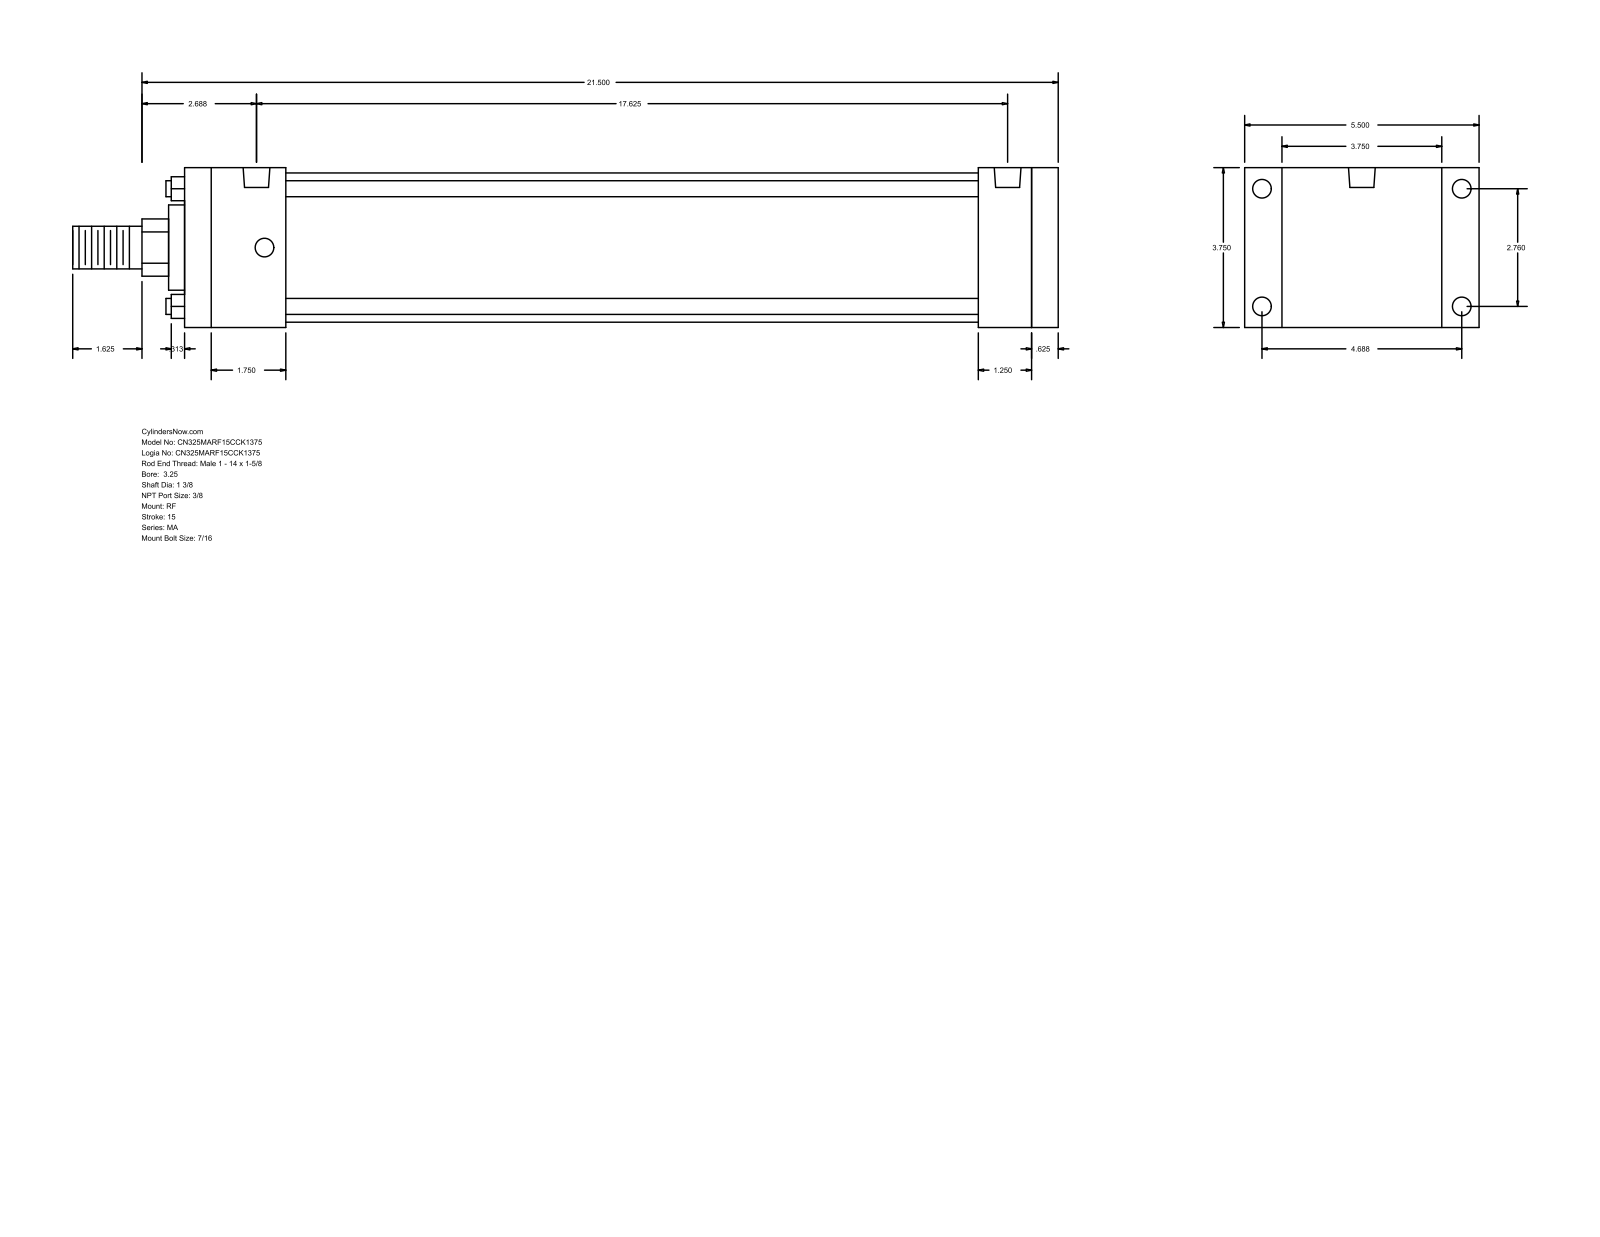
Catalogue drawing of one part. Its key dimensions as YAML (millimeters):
part_name: "MA_RF__0325_1.375"
step_written_by: "GSSL Pune (CONFIG_CONTROL_DESIGN)"
units: millimeters
bodies: {solids: 0, faces: 92, planar: 64, cylindrical: 28, other: 0}
overall_size: [587.38, 139.7, 95.25]
round_holes:
  - {diameter: 11.11, count: 8}
  - {diameter: 15.93, count: 2}
round_bosses_or_shafts:
  - {diameter: 9.53, count: 4}
  - {diameter: 88.9, count: 1}
  - {diameter: 50.8, count: 1}
  - {diameter: 34.92, count: 1}
  - {diameter: 25.4, count: 1}
partial_cylinders:
  - {radius: 17.06, count: 1}
face_to_face_distances: [95.24, 520.7, 504.83, 15.87, 22.23, 117.47, 473.08, 31.75, 47.62, 60.32]
hole_center_spacings: [70.1, 119.06, 138.16, 438.15, 4.76, 4.77, 442.91, 442.92]
